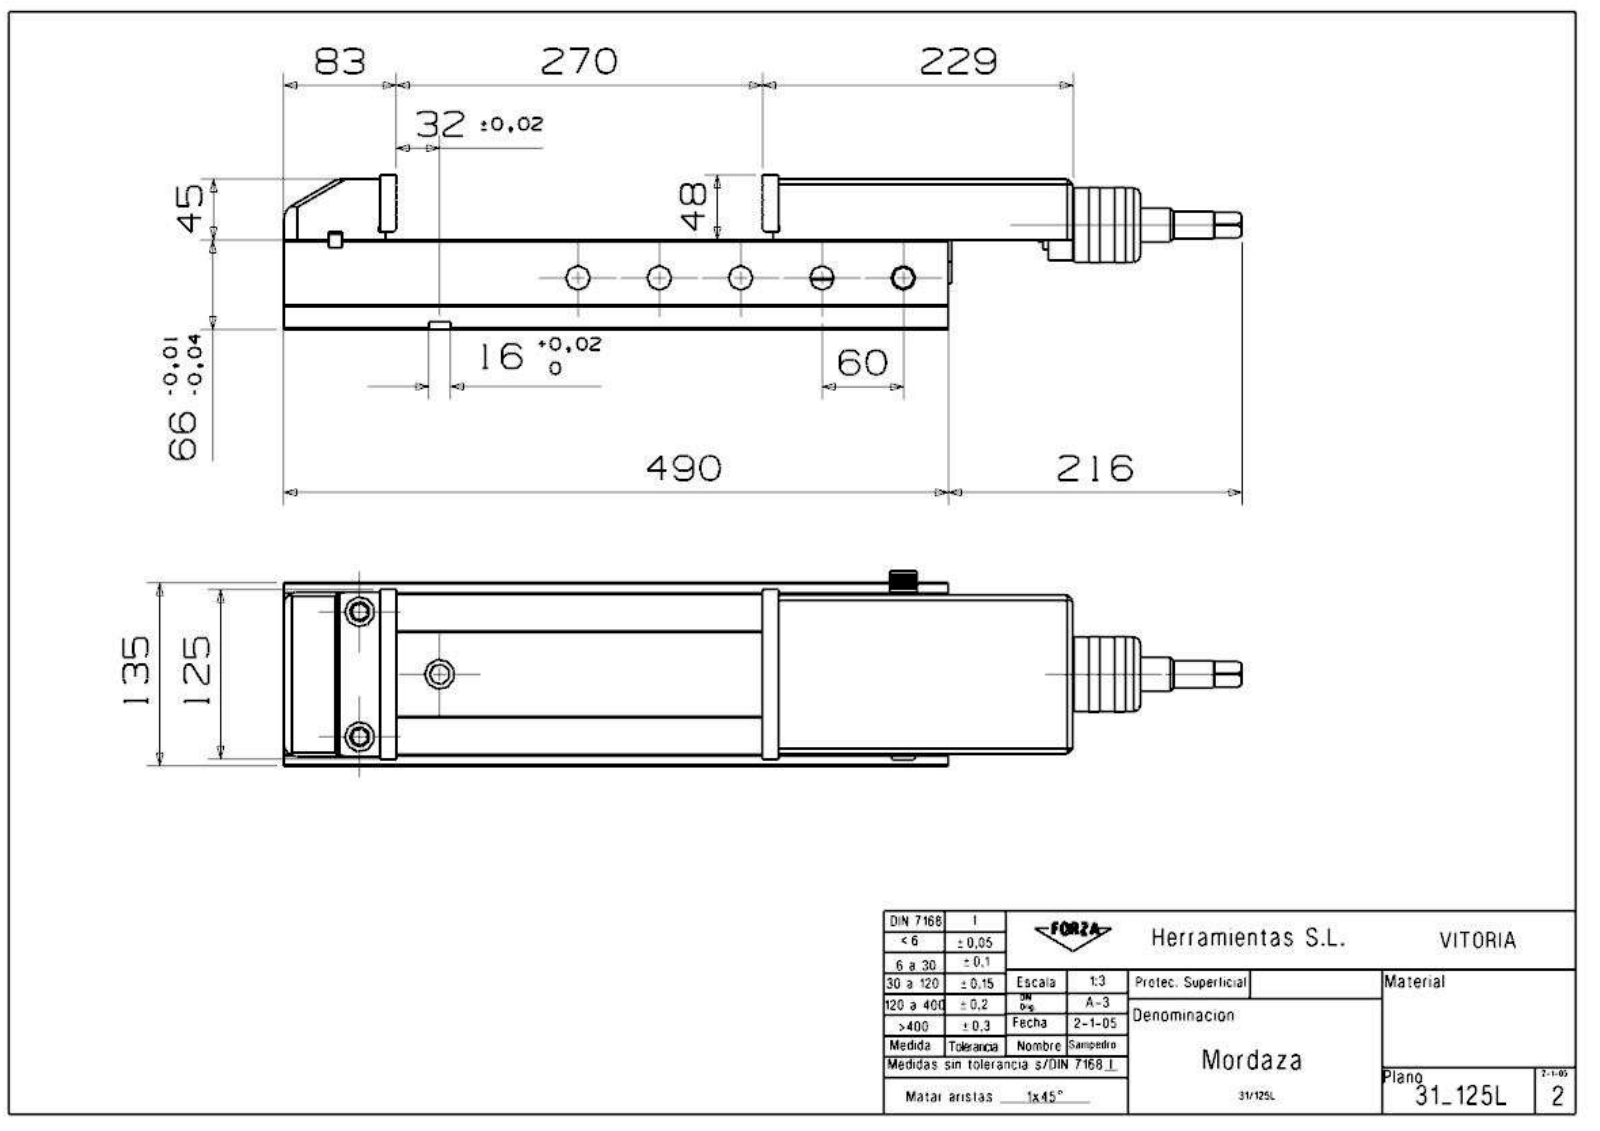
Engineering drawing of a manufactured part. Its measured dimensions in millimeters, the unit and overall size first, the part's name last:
Units: millimetres
Overall size (bounding box): 706.5 × 143.5 × 114
Round holes (diameter × count): ⌀15 ×6, ⌀22 ×6, ⌀18 ×5, ⌀5.19 ×4, ⌀6.99 ×4, ⌀10 ×4, ⌀12.38 ×4, ⌀14 ×4, ⌀3.43 ×2, ⌀4 ×2, ⌀4.5 ×2, ⌀8.5 ×2
Round bosses / shafts (diameter × count): ⌀20 ×2, ⌀55.5 ×1, ⌀55 ×1, ⌀50 ×1, ⌀46 ×1, ⌀35.9 ×1, ⌀25 ×1, ⌀23.9 ×1
Partial cylindrical surfaces — rounded edges, fillets, slot ends (radius × count): R0.8 ×2, R3 ×2, R8 ×2, R10 ×2, R2 ×1, R12 ×1, R25 ×1
Main face-to-face distances: 66, 25.7, 40.3, 22, 45, 111, 85.3, 29.5, 98, 1.5
Hole centre spacings: 60, 120, 16.38, 17.5, 17.76, 24, 28.69, 34.44
Volume: 4 207 000 mm³ · Surface area: 607 205 mm²
Bodies: 18 solids, 549 faces (352 planar, 113 cylindrical, 84 other)
Part name (STEP PRODUCT): 31_125L_Mordaza
STEP written by: SIEMENS PLM Software NX 7.5 (AUTOMOTIVE_DESIGN)
